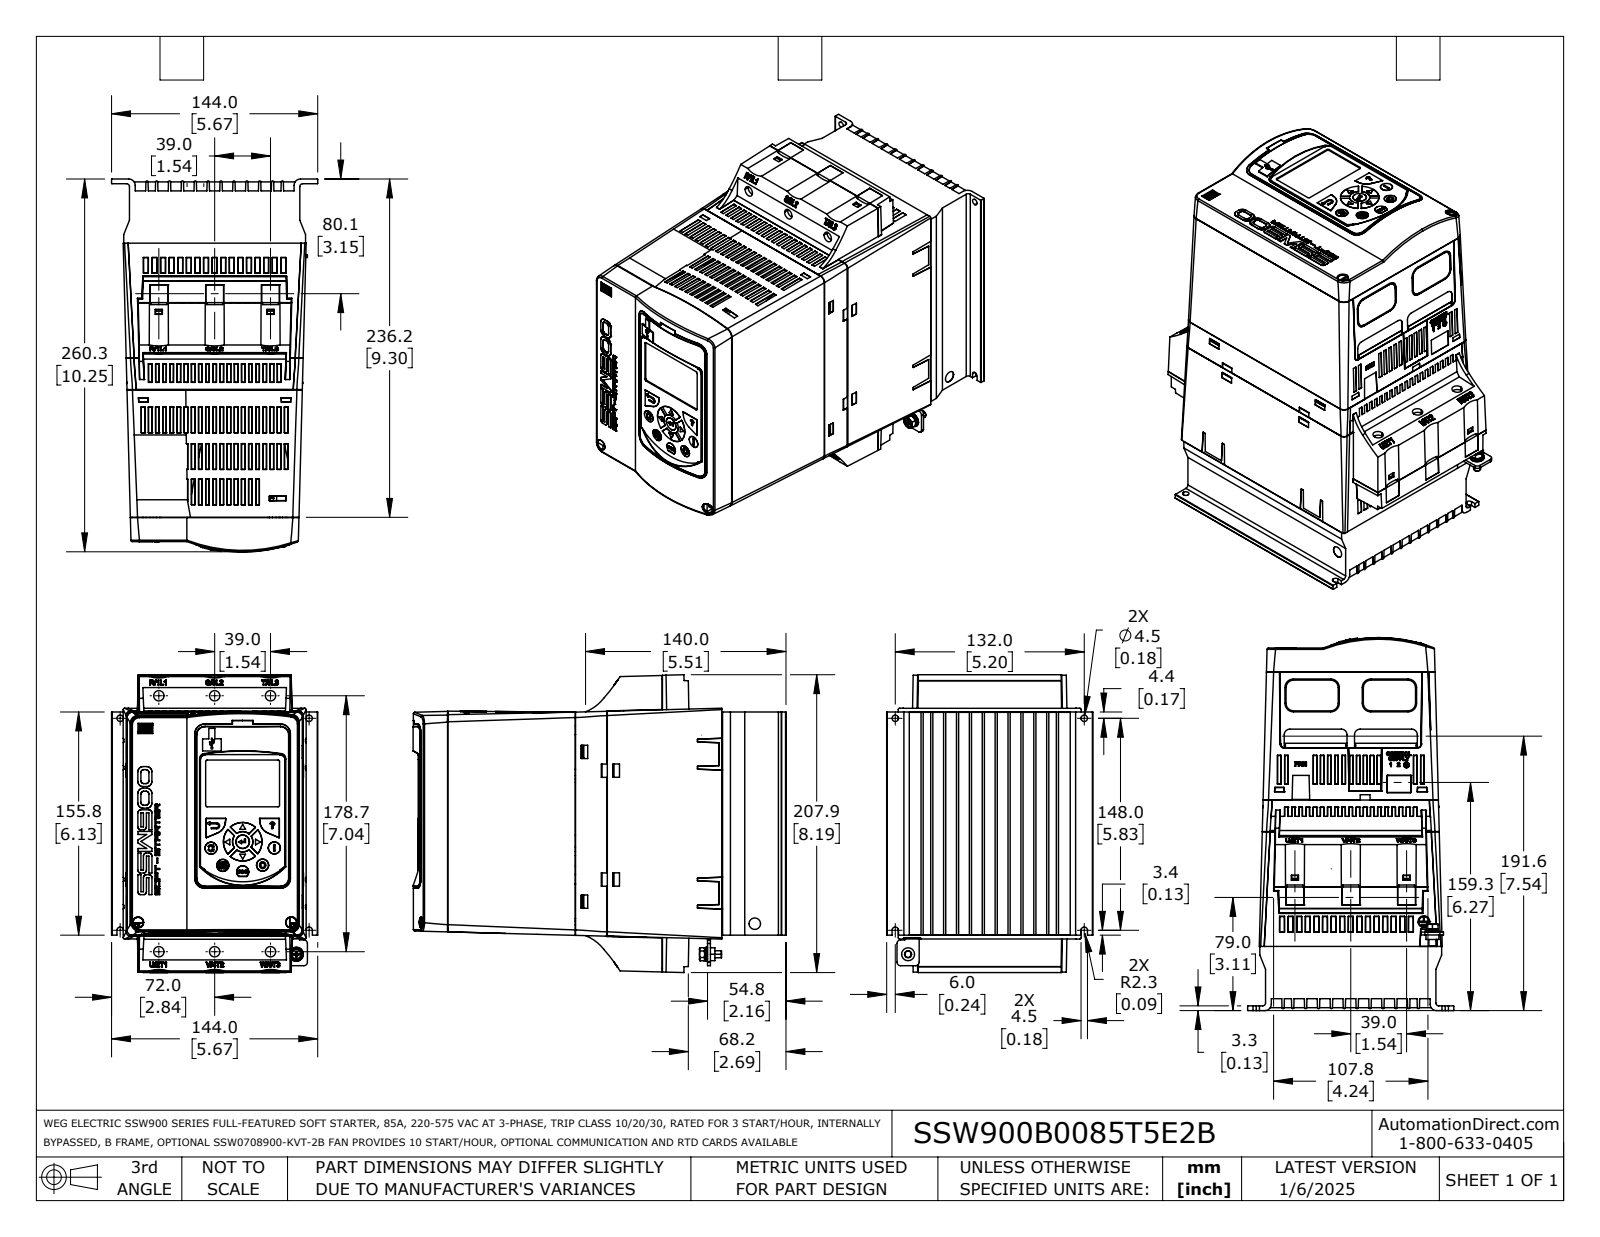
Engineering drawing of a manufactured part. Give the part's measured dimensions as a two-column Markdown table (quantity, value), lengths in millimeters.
| quantity | value |
| --- | --- |
| part name | SSW900B0085T5E2B |
| STEP written by | SolidWorks 2021 (AUTOMOTIVE_DESIGN) |
| units | millimeters |
| bodies | 6 solids, 3794 faces (2929 planar, 209 cylindrical, 656 other) |
| overall size | 260.5 × 207.9 × 144 |
| volume | 5 085 000 mm³ |
| surface area | 281 900 mm² |
| round holes (diameter × count) | 7.2 × 6, 4.5 × 2, 3 × 1, 3.4 × 1, 4.2 × 1, 6.3 × 1, 7 × 1, 7.2 × 1, 8 × 1 |
| round bosses / shafts (diameter × count) | 9.8 × 1, 9 × 1, 8.2 × 1, 8.1 × 1, 6.7 × 1, 5 × 1, 4.9 × 1, 3.8 × 1 |
| partial cylindrical surfaces (radius × count) | 0.3 × 28, 0.2 × 16, 0.8 × 12, 0.5 × 9, 0.2 × 7, 0.4 × 4, 1 × 4, 2.5 × 4 |
| main face-to-face distances | 145, 145.2, 251.1, 106.1, 105.9, 2.5, 155.8, 178, 17.8, 19.9 |
| hole center spacings | 39, 182.9, 178.7, 78, 195, 18.1, 22.5, 25 |
